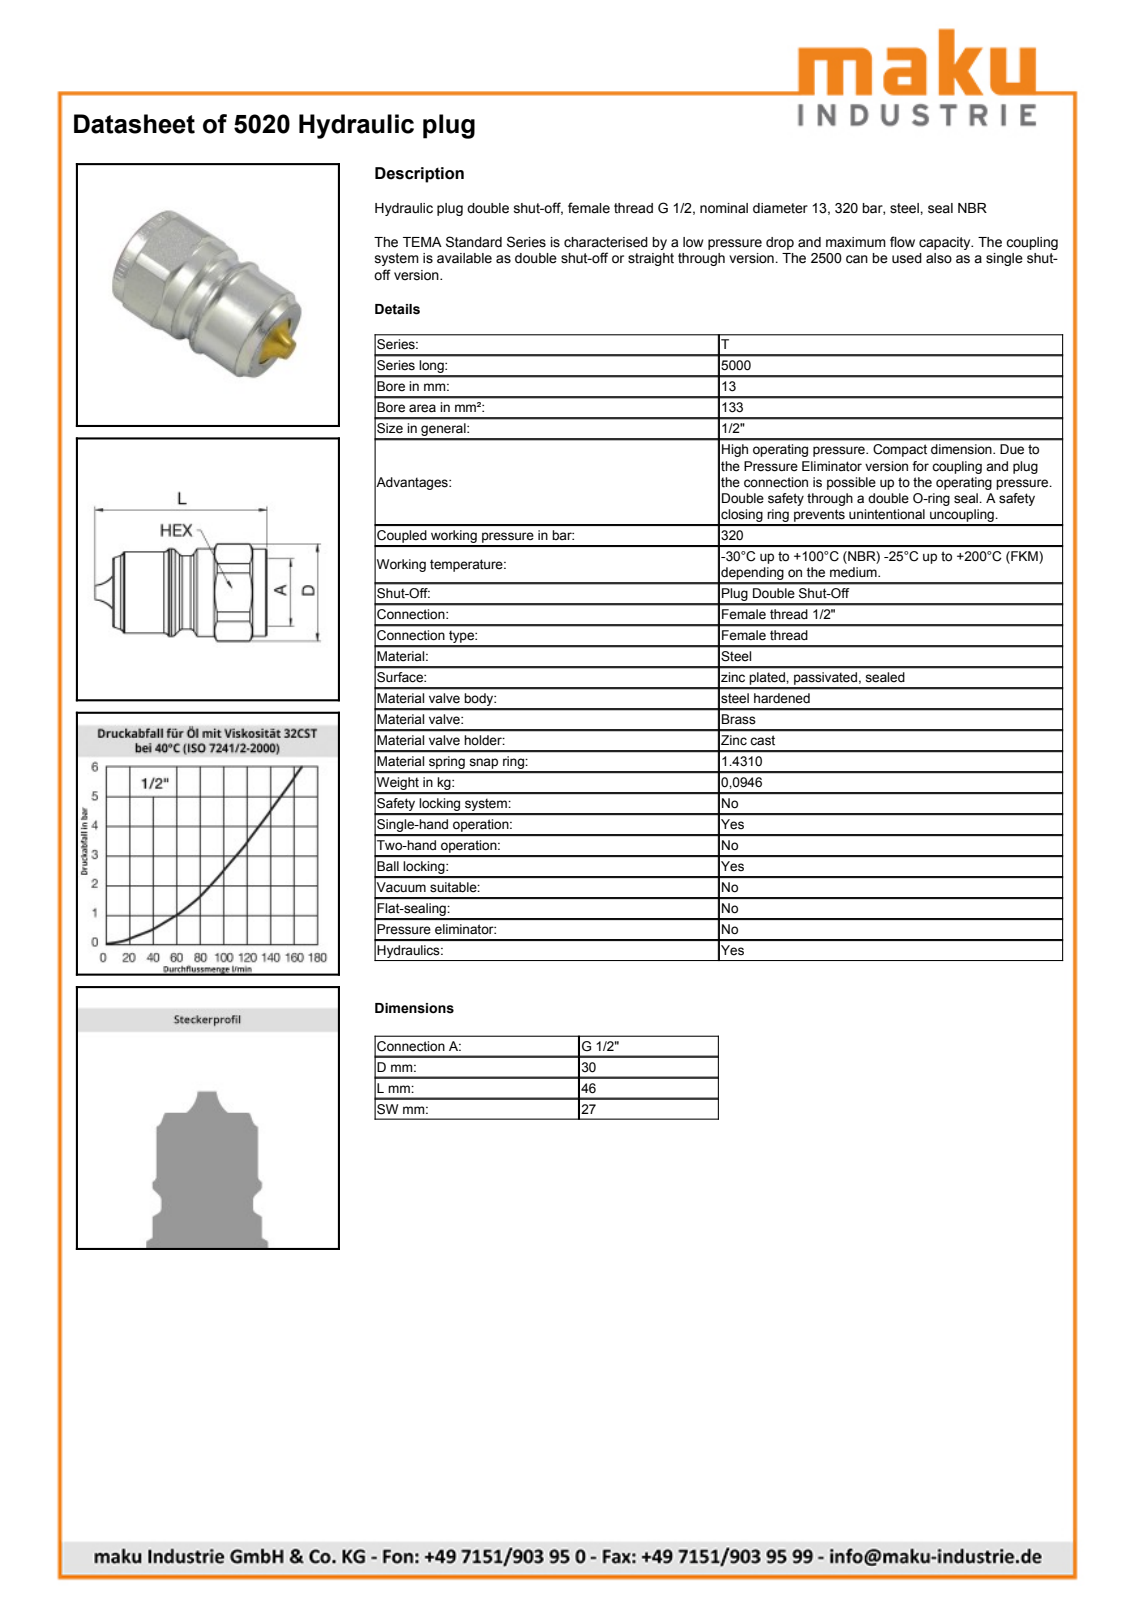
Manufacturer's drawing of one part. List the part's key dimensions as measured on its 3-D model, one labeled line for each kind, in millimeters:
Part name (STEP PRODUCT): 5020
STEP written by: SolidWorks 2009 (AUTOMOTIVE_DESIGN)
Units: millimetres
Bodies: 1 solid, 56 faces (10 planar, 20 cylindrical, 26 other)
Overall size (bounding box): 45.75 × 29.5 × 27
Volume: 17 088 mm³ · Surface area: 5 649 mm²
Round holes (diameter × count): ⌀13.2 ×1, ⌀18.63 ×1
Round bosses / shafts (diameter × count): ⌀26.7 ×1, ⌀24.6 ×1, ⌀22.8 ×1
Partial cylindrical surfaces — rounded edges, fillets, slot ends (radius × count): R14.75 ×1
Main face-to-face distances: 27, 24.25, 41.5, 17.25, 4.25, 28.5, 45.75
